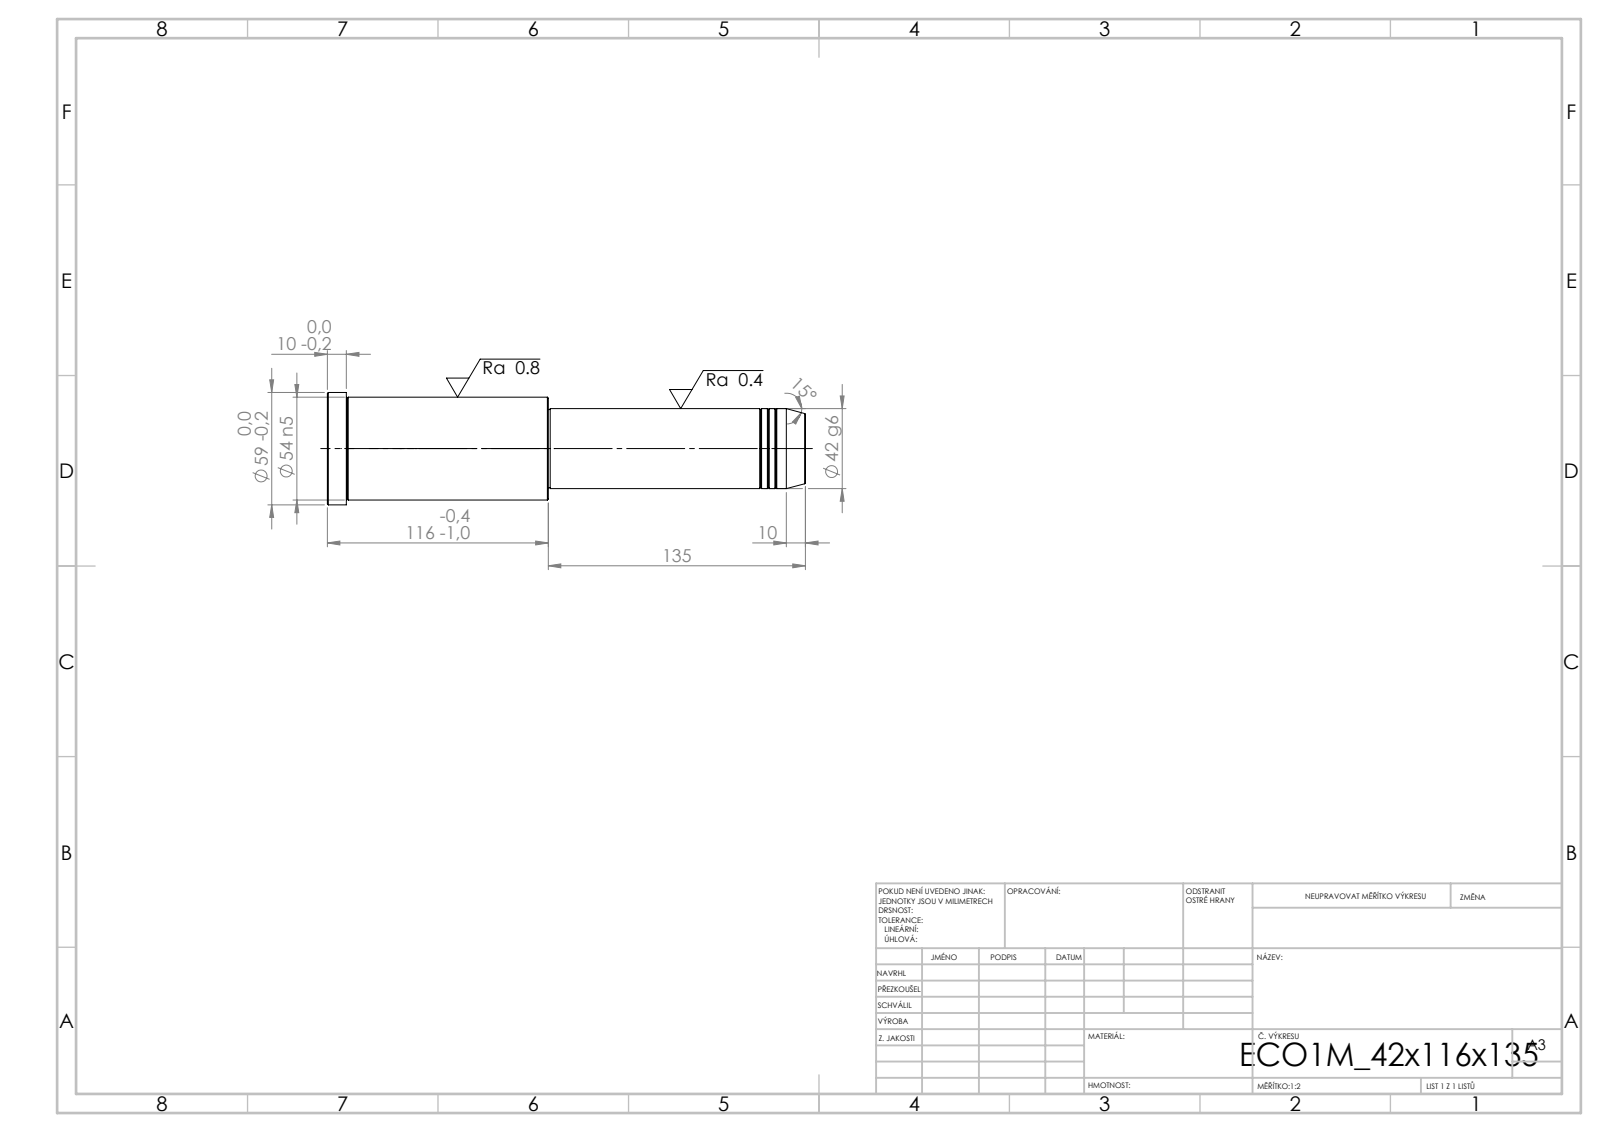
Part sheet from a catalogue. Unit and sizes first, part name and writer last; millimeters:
Units: millimetres
Overall size (bounding box): 251 × 59 × 59
Round bosses / shafts (diameter × count): ⌀59 ×1, ⌀54 ×1, ⌀42 ×1, ⌀41 ×1
Main face-to-face distances: 251, 135, 116, 241, 106, 10, 134, 1, 107, 117
Volume: 455 113 mm³ · Surface area: 43 065 mm²
Bodies: 1 solid, 43 faces (5 planar, 14 cylindrical, 24 other)
STEP written by: SolidWorks 2019 (CONFIG_CONTROL_DESIGN)
